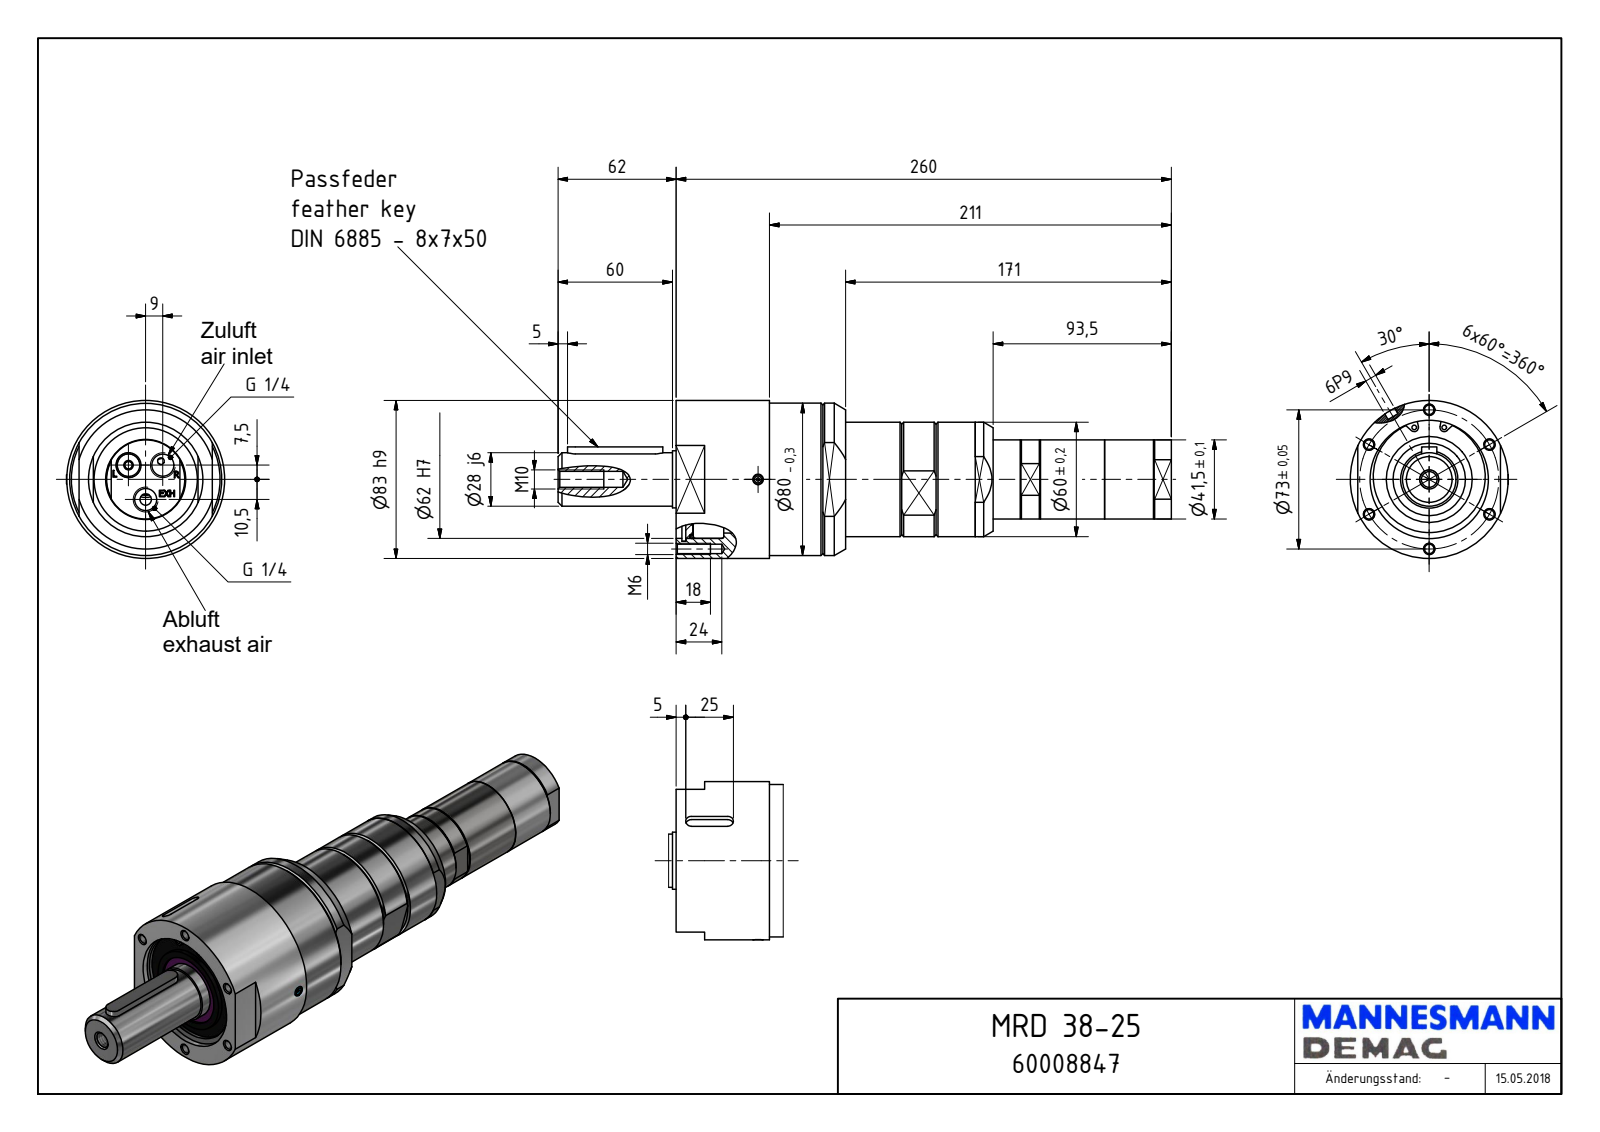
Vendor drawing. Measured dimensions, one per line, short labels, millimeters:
name: MRD 38-25_60008847
written by: Autodesk Inventor 2018 (AUTOMOTIVE_DESIGN)
unit: mm
bodies: 1 solid, 550 faces (232 planar, 257 cylindrical, 61 other)
size: 322 × 83 × 83
volume: 816 379 mm³; area: 78 290 mm²
holes: 6× ⌀4.92, 3× ⌀1.55, 3× ⌀4, 3× ⌀11.45, 2× ⌀5.5, 1× ⌀8.38, 1× ⌀38, 1× ⌀42, 1× ⌀62, 1× ⌀65, 1× ⌀67.4
bosses: 2× ⌀5, 2× ⌀3.6, 1× ⌀83, 1× ⌀80, 1× ⌀67, 1× ⌀60, 1× ⌀45, 1× ⌀41.5
rounds: 94× R3.5, 2× R3, 2× R4, 1× R19.49, 1× R24.63, 1× R24.96, 1× R39.46
face distances: 2.5, 5, 84, 89, 260, 255, 171, 77.5, 166.5, 161.5
hole spacings: 36.5, 63.22, 73, 11.72, 20.12, 25.04, 30.36, 32.55
